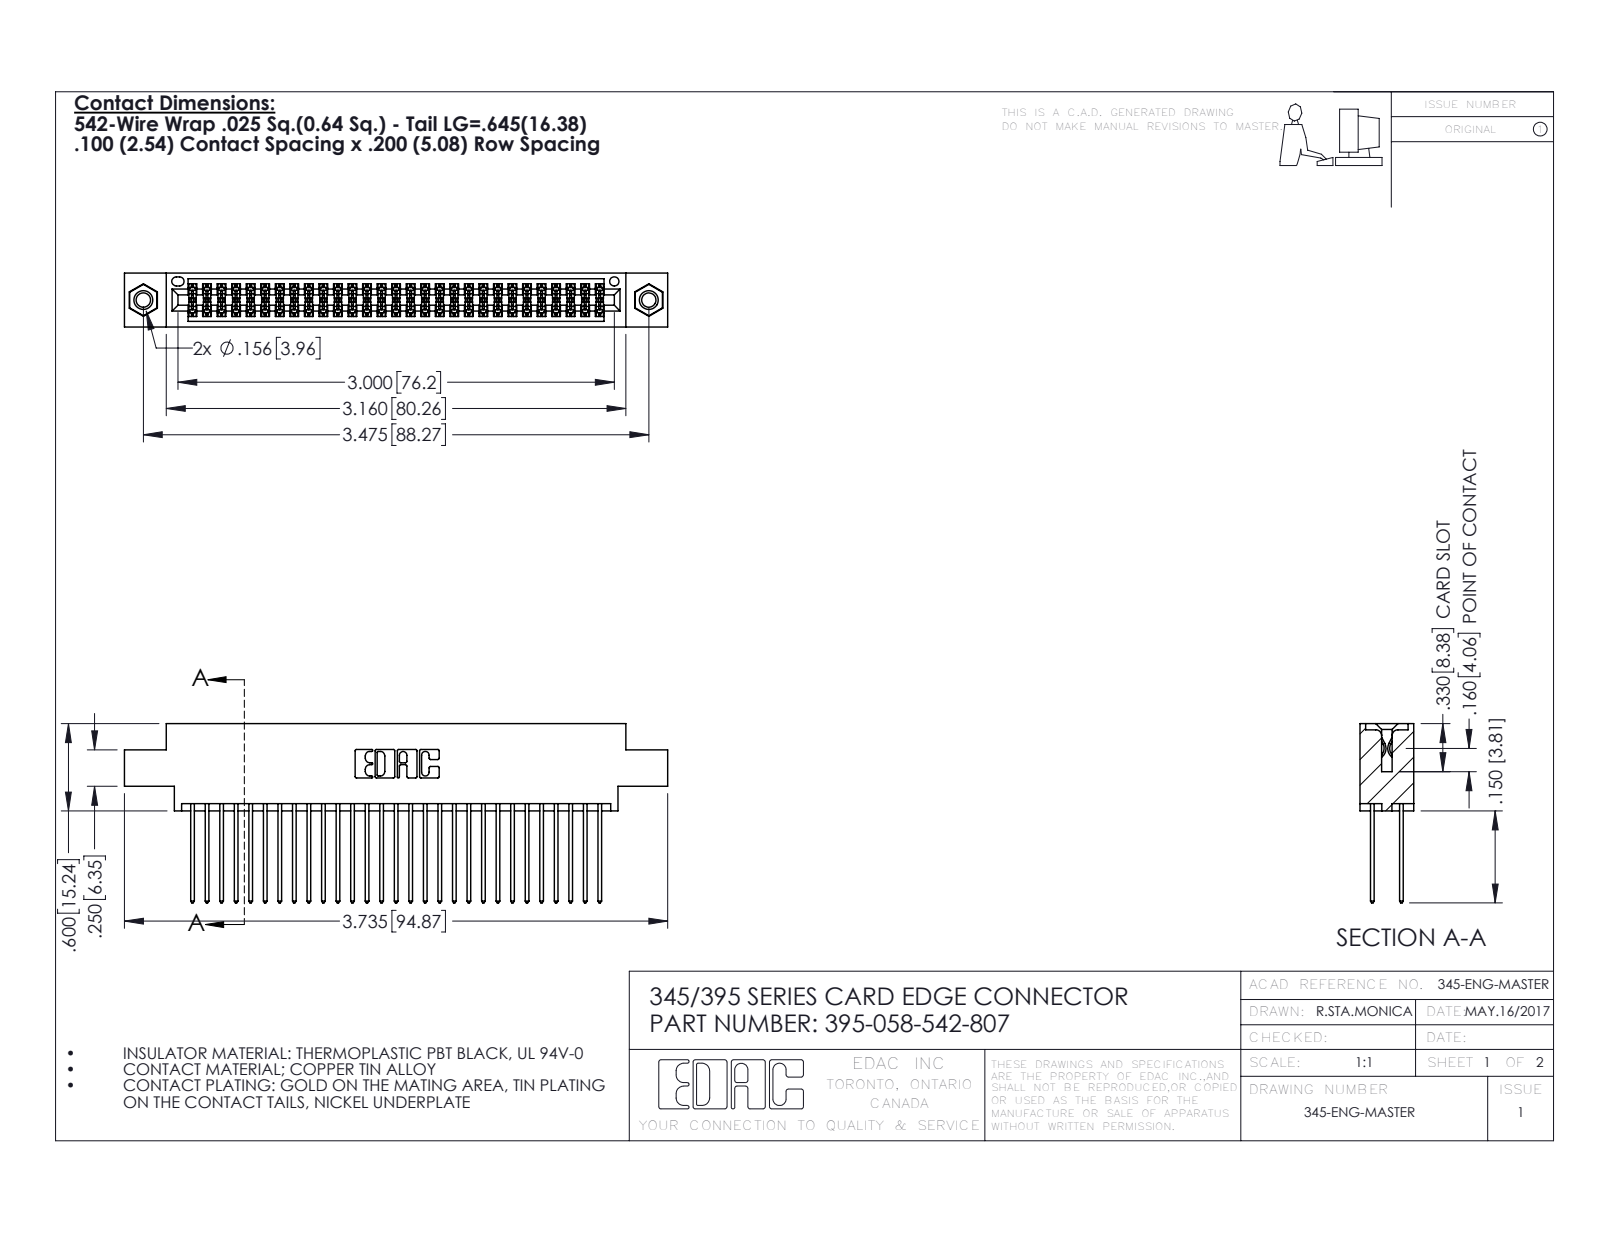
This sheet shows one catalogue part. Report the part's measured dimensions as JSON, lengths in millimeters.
{"part_name": "345 Part_0.170 Offset - 0.156 Dia-TI; 345-250-001_345-250-005-103; 395-058-542-807; 345-292-001_345-293-142", "step_written_by": "SolidWorks 2016 (CONFIG_CONTROL_DESIGN)", "units": "millimeters", "bodies": {"solids": 61, "faces": 3090, "planar": 2030, "cylindrical": 1044, "other": 16}, "overall_size": [94.9, 31.3, 9.4], "volume_mm3": 9240, "surface_area_mm2": 14840, "round_holes": [[2.5, 2], [3.2, 2], [4, 2], [1.6, 1]], "round_bosses_or_shafts": [[3.9, 2]], "partial_cylinders_radius": [[0.2, 87], [0.3, 58], [0.3, 22], [0.2, 6], [0.8, 6], [0.7, 3], [0.4, 2], [0.5, 2]], "face_to_face_distances": [1.8, 7.6, 5.1, 2.5, 6.9, 0.6, 9.4, 5.7, 4.4, 3.8], "hole_center_spacings": [6.9, 82.3, 88.3]}
